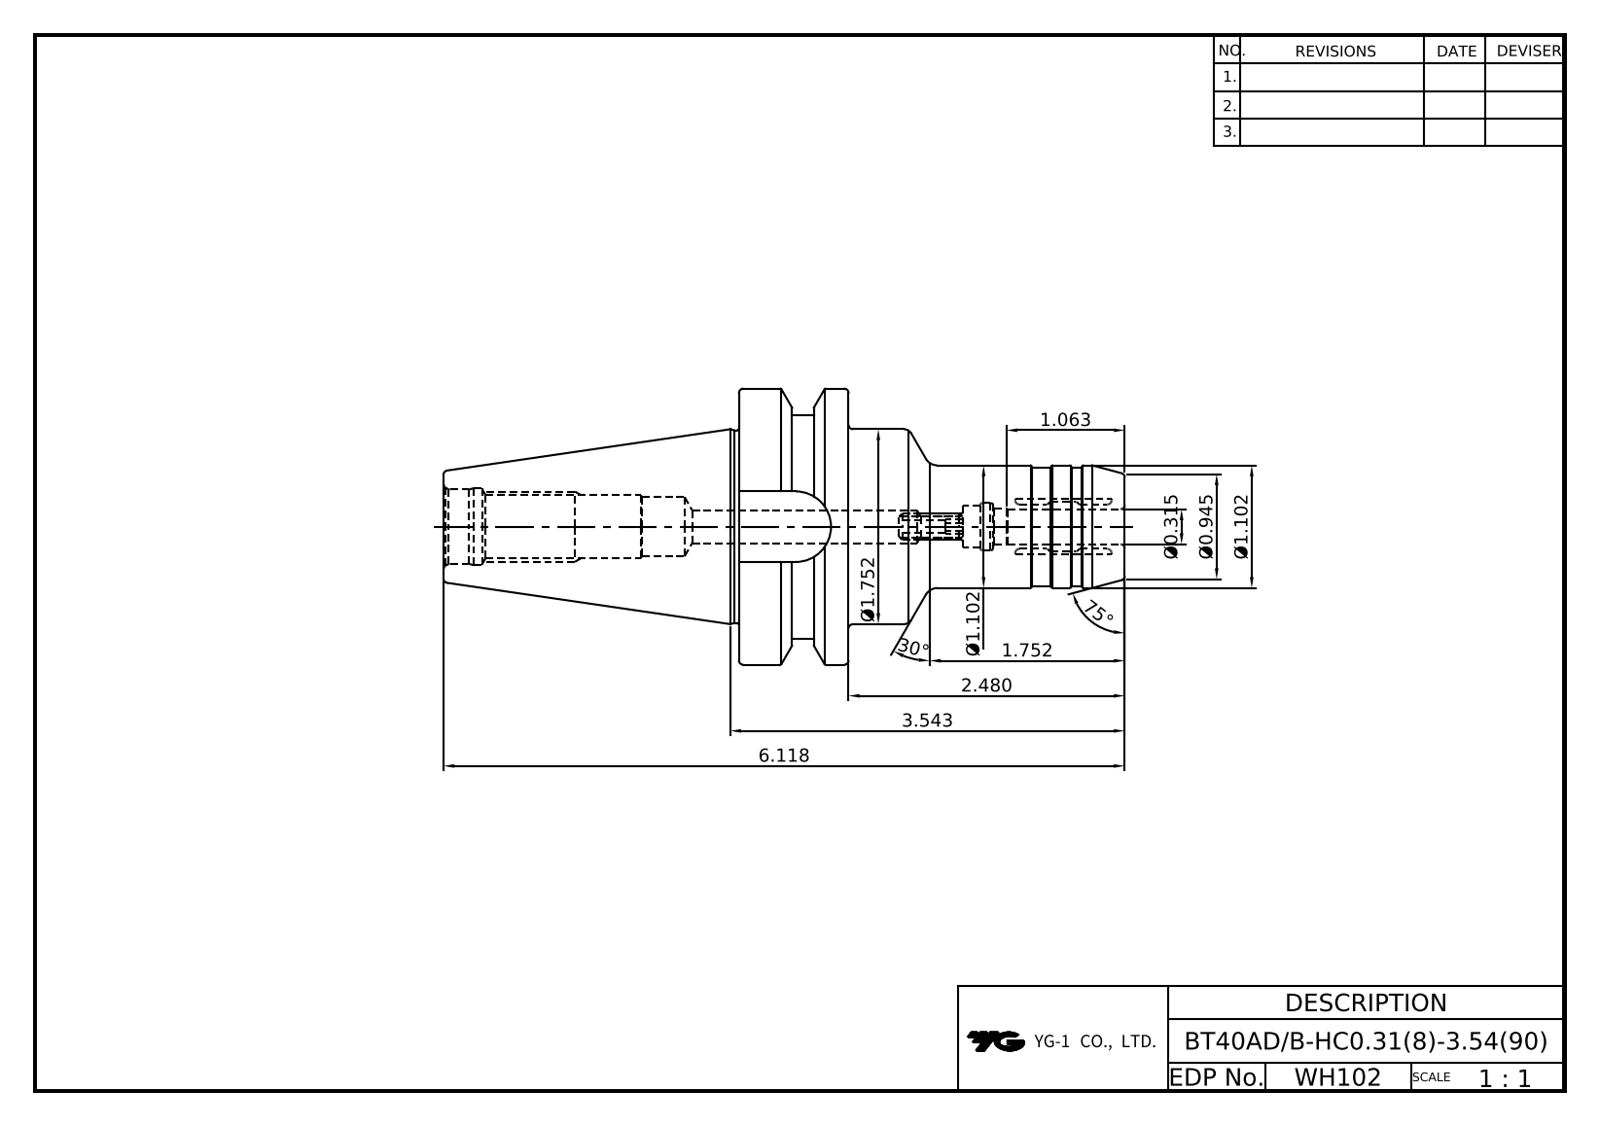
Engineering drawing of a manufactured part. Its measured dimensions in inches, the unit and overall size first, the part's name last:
Units: inches
Overall size (bounding box): 6.118 × 2.48 × 2.48
Round holes (diameter × count): ⌀0.128 ×4, ⌀0.157 ×4, ⌀0.194 ×1, ⌀0.295 ×1, ⌀0.315 ×1, ⌀0.339 ×1, ⌀0.531 ×1, ⌀0.545 ×1, ⌀0.669 ×1, ⌀0.693 ×1
Round bosses / shafts (diameter × count): ⌀2.48 ×1, ⌀2.008 ×1, ⌀1.752 ×1, ⌀1.732 ×1, ⌀1.102 ×1, ⌀1.063 ×1
Partial cylindrical surfaces — rounded edges, fillets, slot ends (radius × count): R0.317 ×1
Main face-to-face distances: 0.984, 3.465, 2.48, 1.78, 0.673, 0.311, 2.791, 0.476, 0.197, 0.508
Volume: 10.51 in³ · Surface area: 46.65 in²
Bodies: 1 solid, 90 faces (21 planar, 34 cylindrical, 35 other)
Part name (STEP PRODUCT): LO-BT40ADB-HC8-90
STEP written by: Autodesk Inventor 2022 (AUTOMOTIVE_DESIGN)
